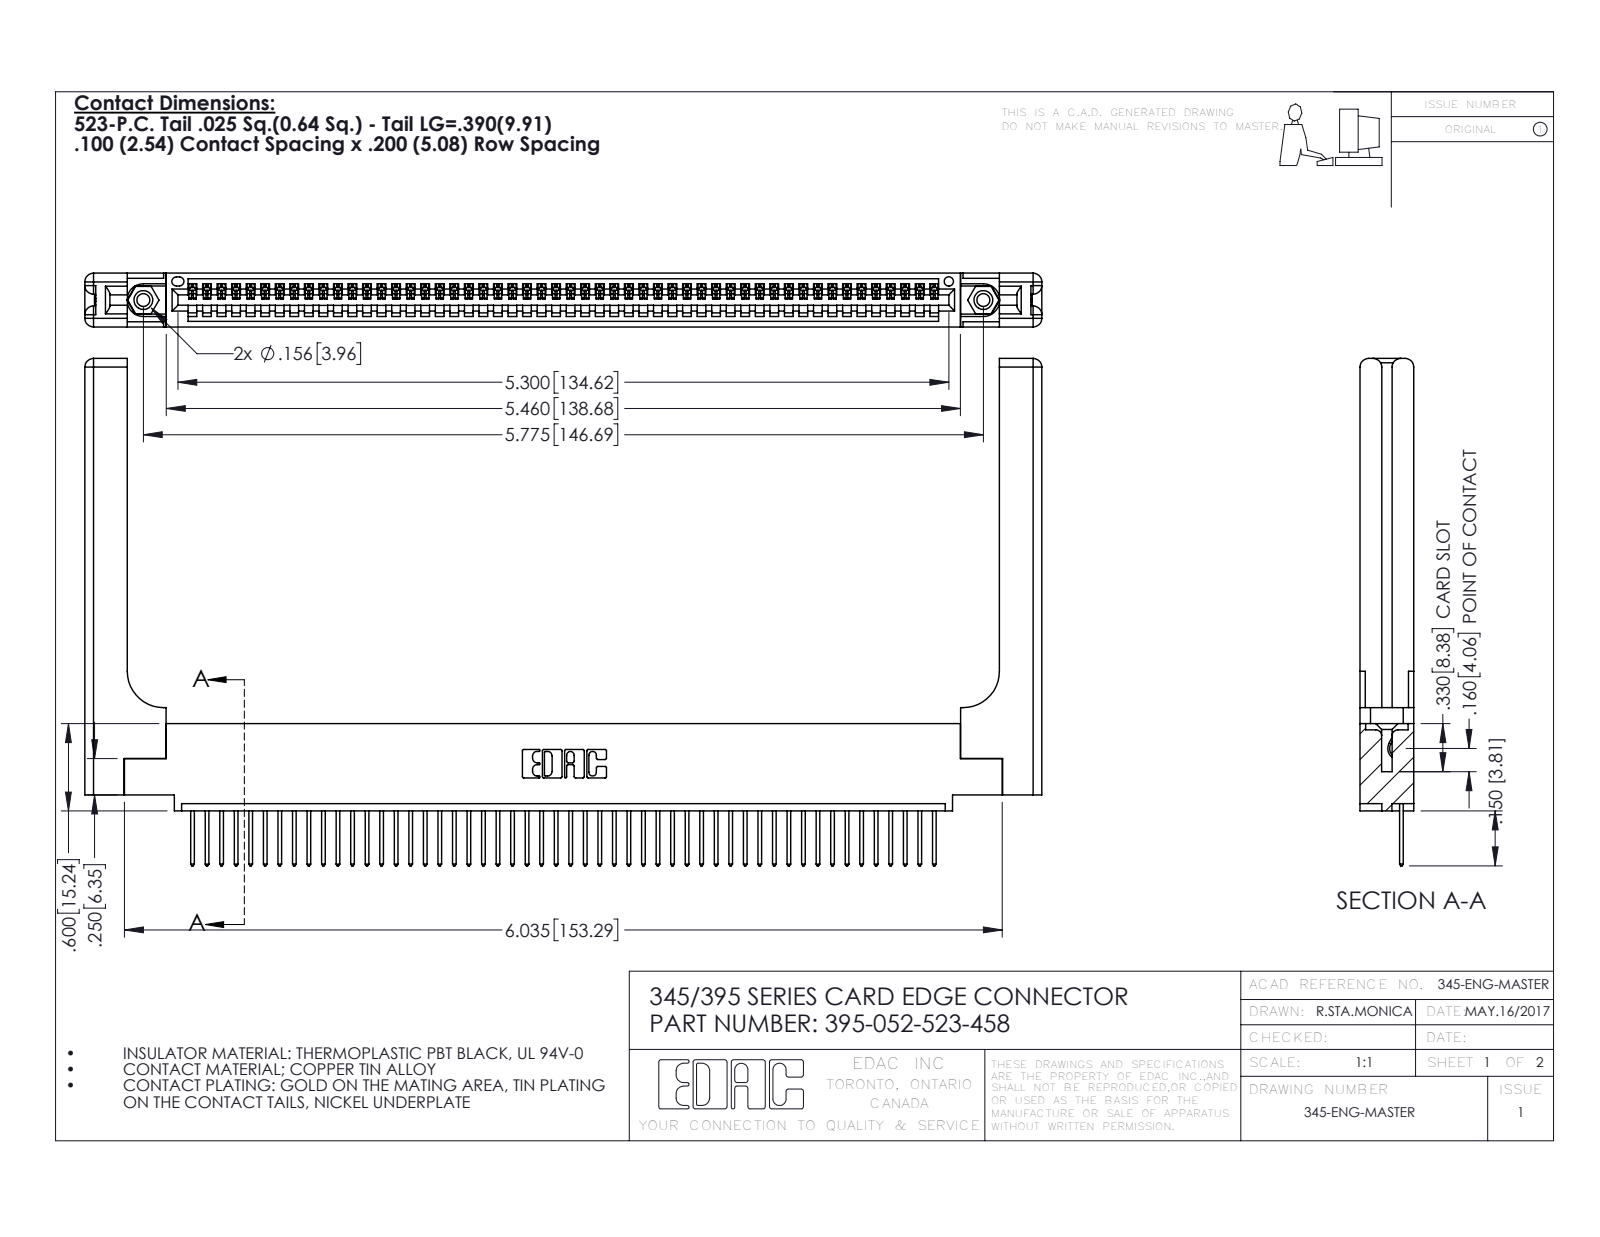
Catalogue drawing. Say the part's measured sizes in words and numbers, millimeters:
The part is named "345-250-001_345-250-001-102; 345-220-058_345-220-058; 395-052-523-458; 345-292-001_345-293-123 (+1 more)". Its 3-D file was written by "SolidWorks 2016 (CONFIG_CONTROL_DESIGN)". It is 57 solids with 3402 faces: 2312 planar, 1030 cylindrical and 60 other. Overall it measures 167.1 by 88.6 by 9.4 millimeters. Its volume is 24 370 cubic millimeters and its surface area 26 660 square millimeters. Round holes: 2 of diameter 2.3, 2 of diameter 3.2, 2 of diameter 4, 1 of diameter 1.6. Round bosses or shafts: 2 of diameter 3.9. Partial cylindrical surfaces (rounded edges, fillets, slot ends): 104 of radius 0.2, 104 of radius 0.3, 22 of radius 0.3, 16 of radius 1.5, 6 of radius 0.2, 6 of radius 0.8, 3 of radius 0.7, 2 of radius 0.8. The main face-to-face distances are 1.8, 9.4, 7.6, 2.5, 6.9, 0.6, 5.1, 5.7, 3.8, 3.8. The hole center spacings are 6.9, 140.7, 146.7.
